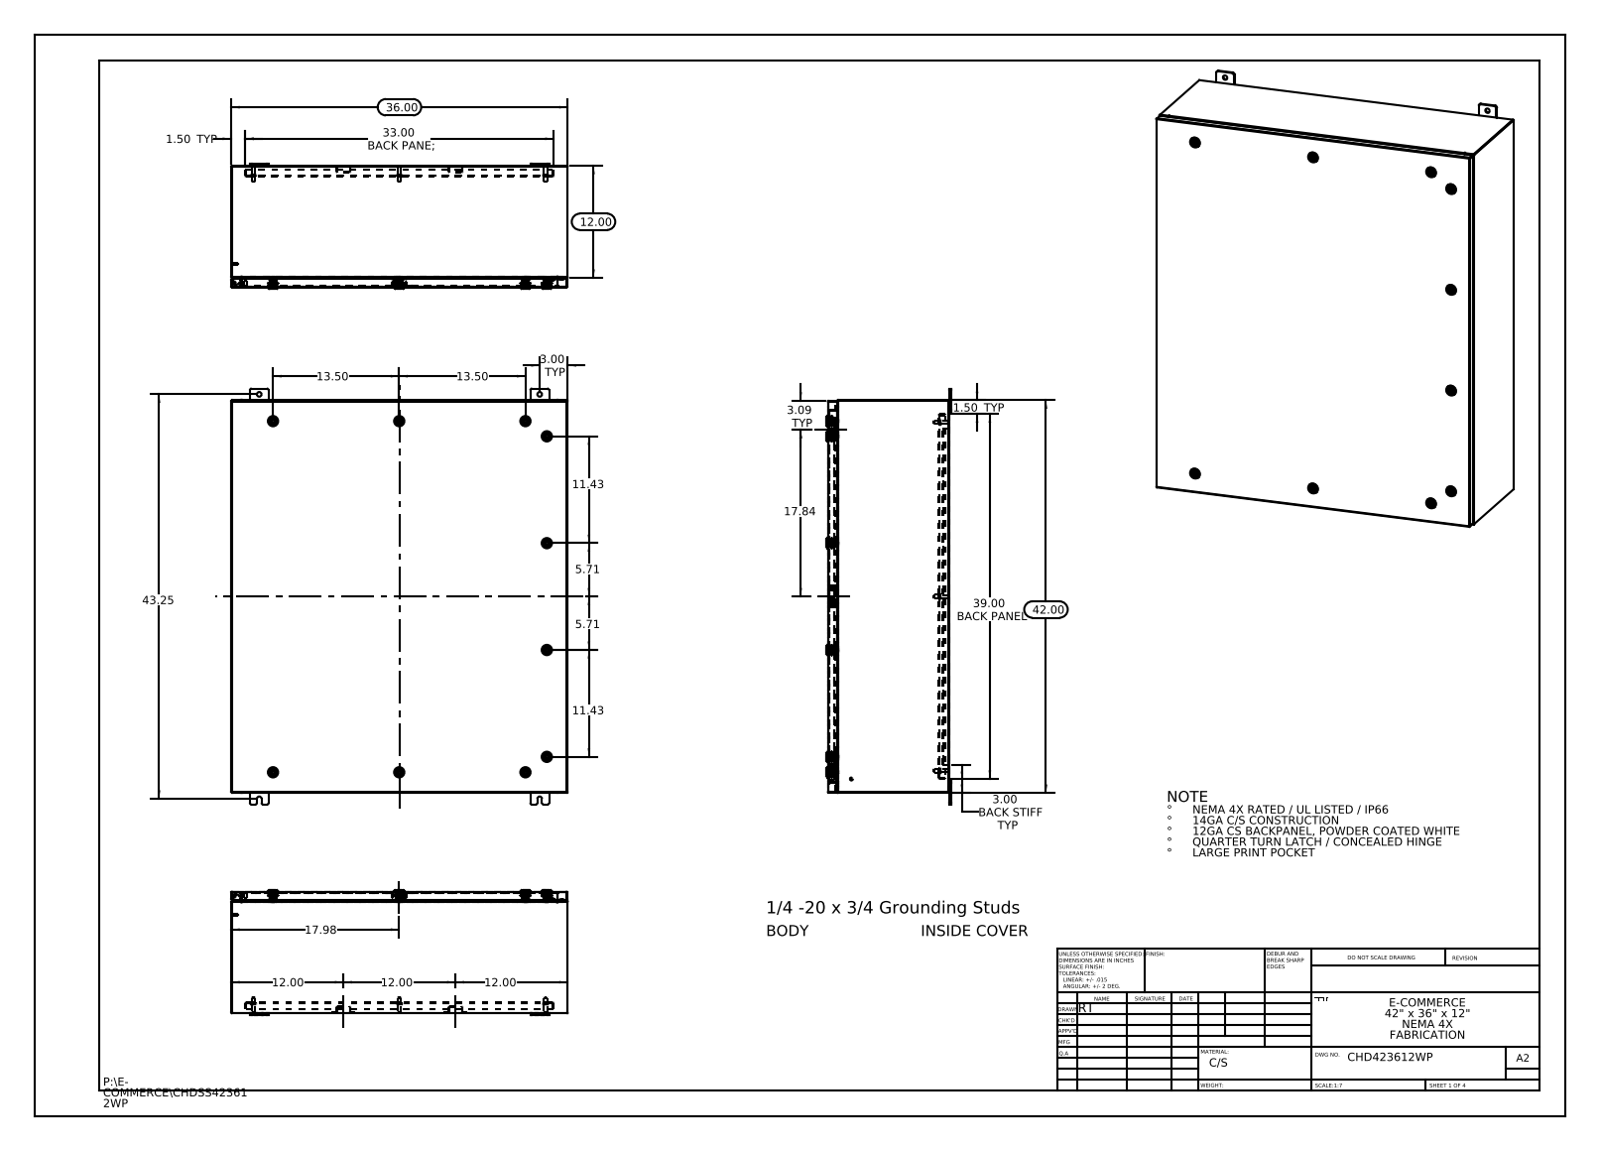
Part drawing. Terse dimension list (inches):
name: CHDSS423612WP Mounting Feet; HW-CLH-E5-8004_Cam-232112-U-Industrilas; CHDSS423612WP Door Stiffener; HW-CLH-R001-0500_2412-026240-2445-Industrilas (+8 more)
written by: SolidWorks 2013 (CONFIG_CONTROL_DESIGN)
unit: in
bodies: 94 solids, 9060 faces (2626 planar, 2826 cylindrical, 3608 other)
size: 44.5 × 36 × 13.356
volume: 581.5 in³; area: 14 474 in²
holes: 12× ⌀0.5, 10× ⌀0.197, 10× ⌀0.394, 10× ⌀0.4, 10× ⌀0.63, 10× ⌀0.787, 6× ⌀0.136, 6× ⌀0.25, 1× ⌀0.211
bosses: 12× ⌀0.236, 10× ⌀1.102, 10× ⌀0.78, 10× ⌀0.626, 10× ⌀0.61, 10× ⌀0.531, 10× ⌀0.392, 10× ⌀0.114
rounds: 330× R0.006, 330× R0.118, 120× R0.028, 40× R0.02, 40× R0.197, 34× R0.013, 30× R0.088, 24× R0.19
face distances: 0.075, 0.074, 12.861, 12.936, 13.01, 12.935, 0.104, 1, 1.075, 11.861
hole spacings: 13.5, 17, 17.145, 18.625, 24.311, 36.379, 39.903, 40.394
